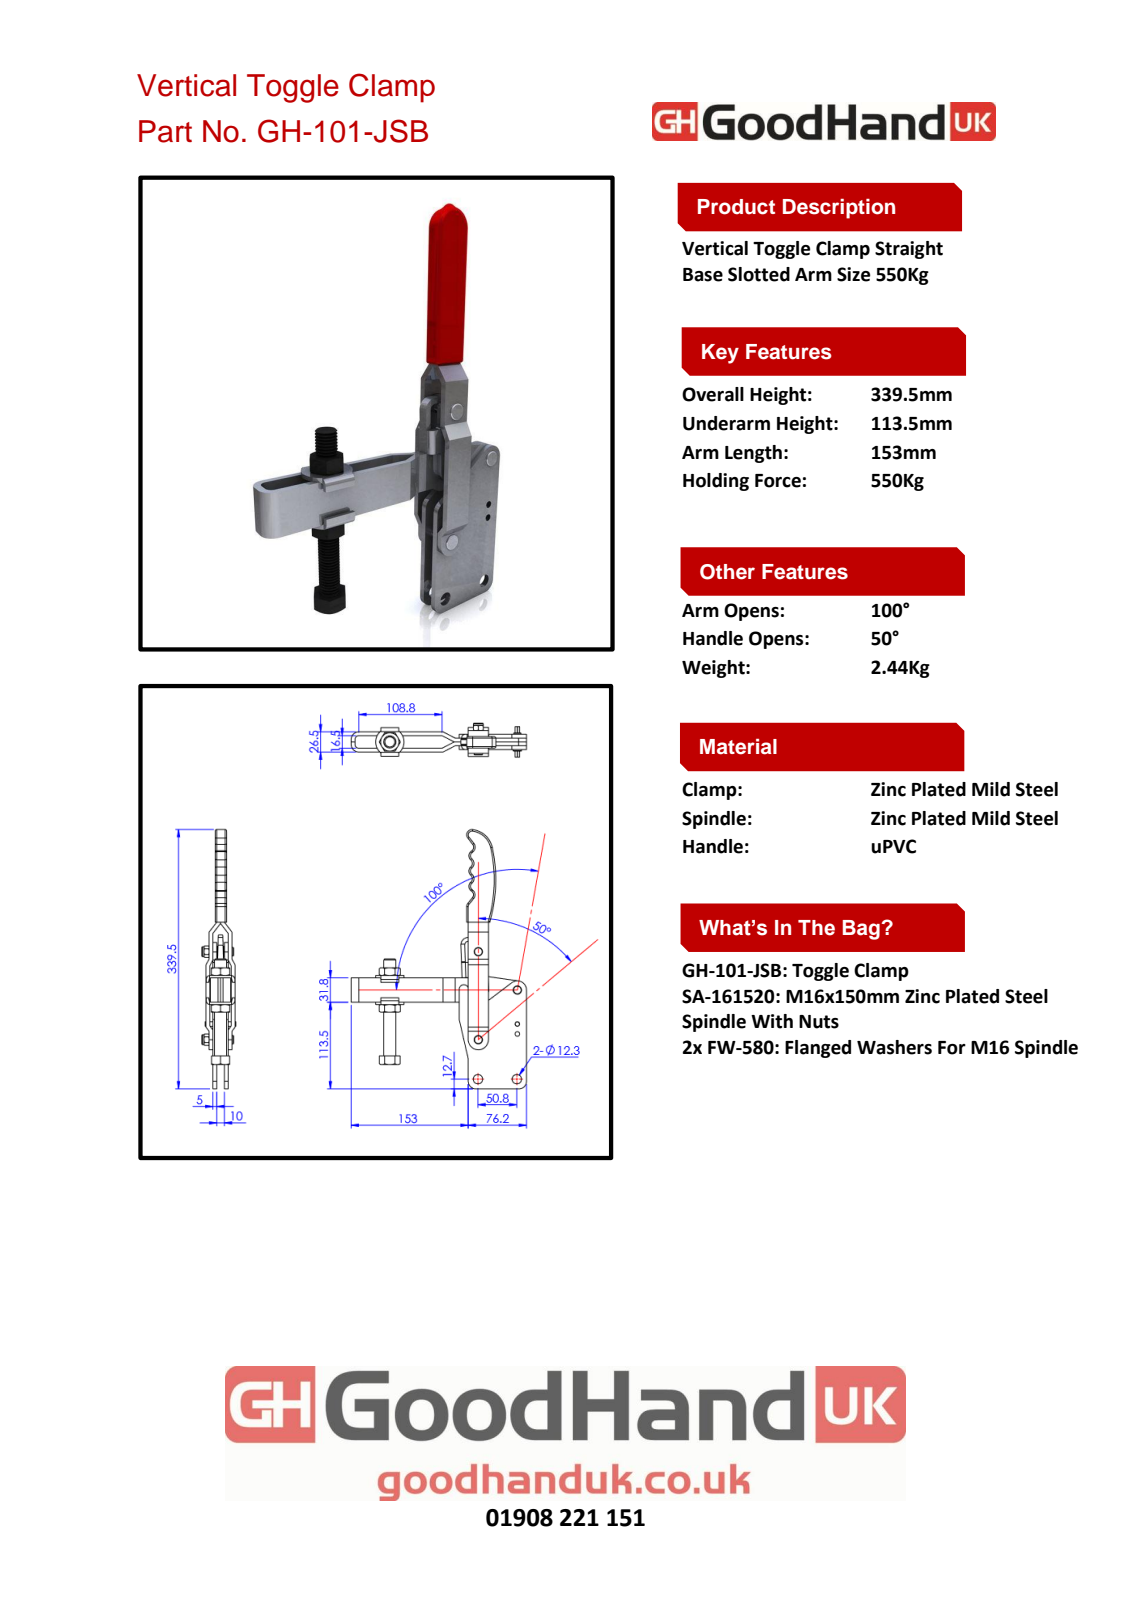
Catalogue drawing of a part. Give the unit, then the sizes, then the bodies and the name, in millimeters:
Units: millimetres
Overall size (bounding box): 339.2 × 229.2 × 40
Round holes (diameter × count): ⌀6 ×5, ⌀12.3 ×2, ⌀5.5 ×1
Round bosses / shafts (diameter × count): ⌀11 ×4, ⌀8 ×2, ⌀7.94 ×2, ⌀24 ×1, ⌀16 ×1, ⌀6 ×1
Partial cylindrical surfaces — rounded edges, fillets, slot ends (radius × count): R2 ×4, R5 ×4, R5.2 ×4, R10 ×4, R12 ×3, R3 ×2, R11 ×2, R6 ×1
Main face-to-face distances: 5, 15, 10, 20, 3.25, 18.25, 23.25, 1.75, 24, 5.75
Hole centre spacings: 13, 44.48, 49.25, 50.23, 50.8, 51.55, 51.7, 54.97
Volume: 243 534 mm³ · Surface area: 137 950 mm²
Bodies: 4 solids, 364 faces (160 planar, 122 cylindrical, 82 other)
Part name (STEP PRODUCT): GH-101-JSB(簡化); Group5^GH-101-JSB(簡化); Group3^GH-101-JSB(簡化); Group1^GH-101-JSB(簡化) (+2 more)
STEP written by: SolidWorks 2016 (AUTOMOTIVE_DESIGN)
